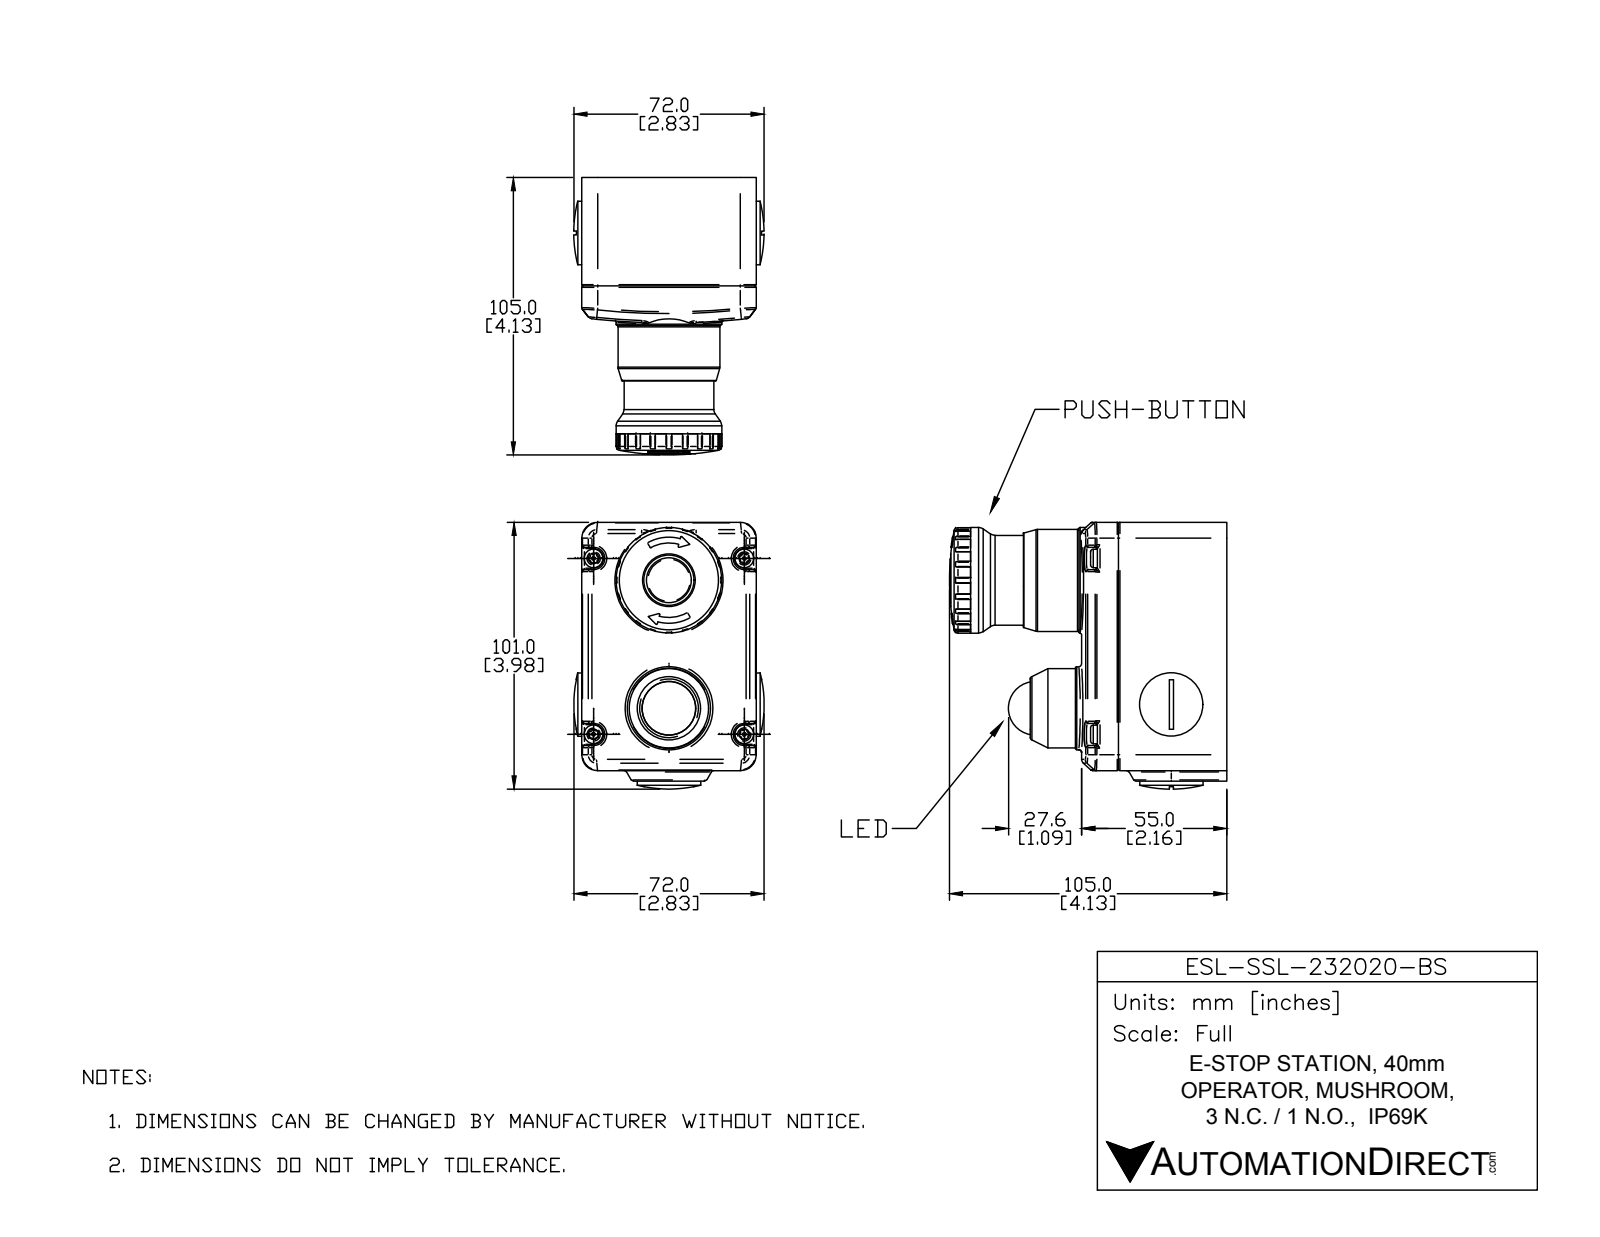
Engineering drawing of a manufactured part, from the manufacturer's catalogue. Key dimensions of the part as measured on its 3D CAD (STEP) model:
Part name (STEP PRODUCT): ESL-SSL-232020-BS
STEP written by: SolidWorks 2016 (AUTOMOTIVE_DESIGN)
Units: millimetres
Bodies: 13 solids, 695 faces (221 planar, 256 cylindrical, 218 other)
Overall size (bounding box): 105 × 100.99 × 71.98
Volume: 369 953 mm³ · Surface area: 65 813 mm²
Round holes (diameter × count): ⌀4.5 ×4, ⌀28.04 ×1, ⌀31.1 ×1, ⌀37 ×1
Round bosses / shafts (diameter × count): ⌀7 ×4, ⌀1 ×4, ⌀24 ×2, ⌀40 ×1, ⌀38.6 ×1, ⌀34 ×1, ⌀31.4 ×1, ⌀30 ×1
Partial cylindrical surfaces — rounded edges, fillets, slot ends (radius × count): R0.1 ×80, R0.76 ×24, R0.5 ×14, R0.2 ×4, R1 ×4, R4.2 ×4, R6 ×4, R2 ×2
Main face-to-face distances: 41, 66, 56, 15, 98, 4, 94, 56.8, 15.8, 0.8
Hole centre spacings: 31.38, 32.23, 54, 69.83, 71.31, 82, 98.18, 48.4
